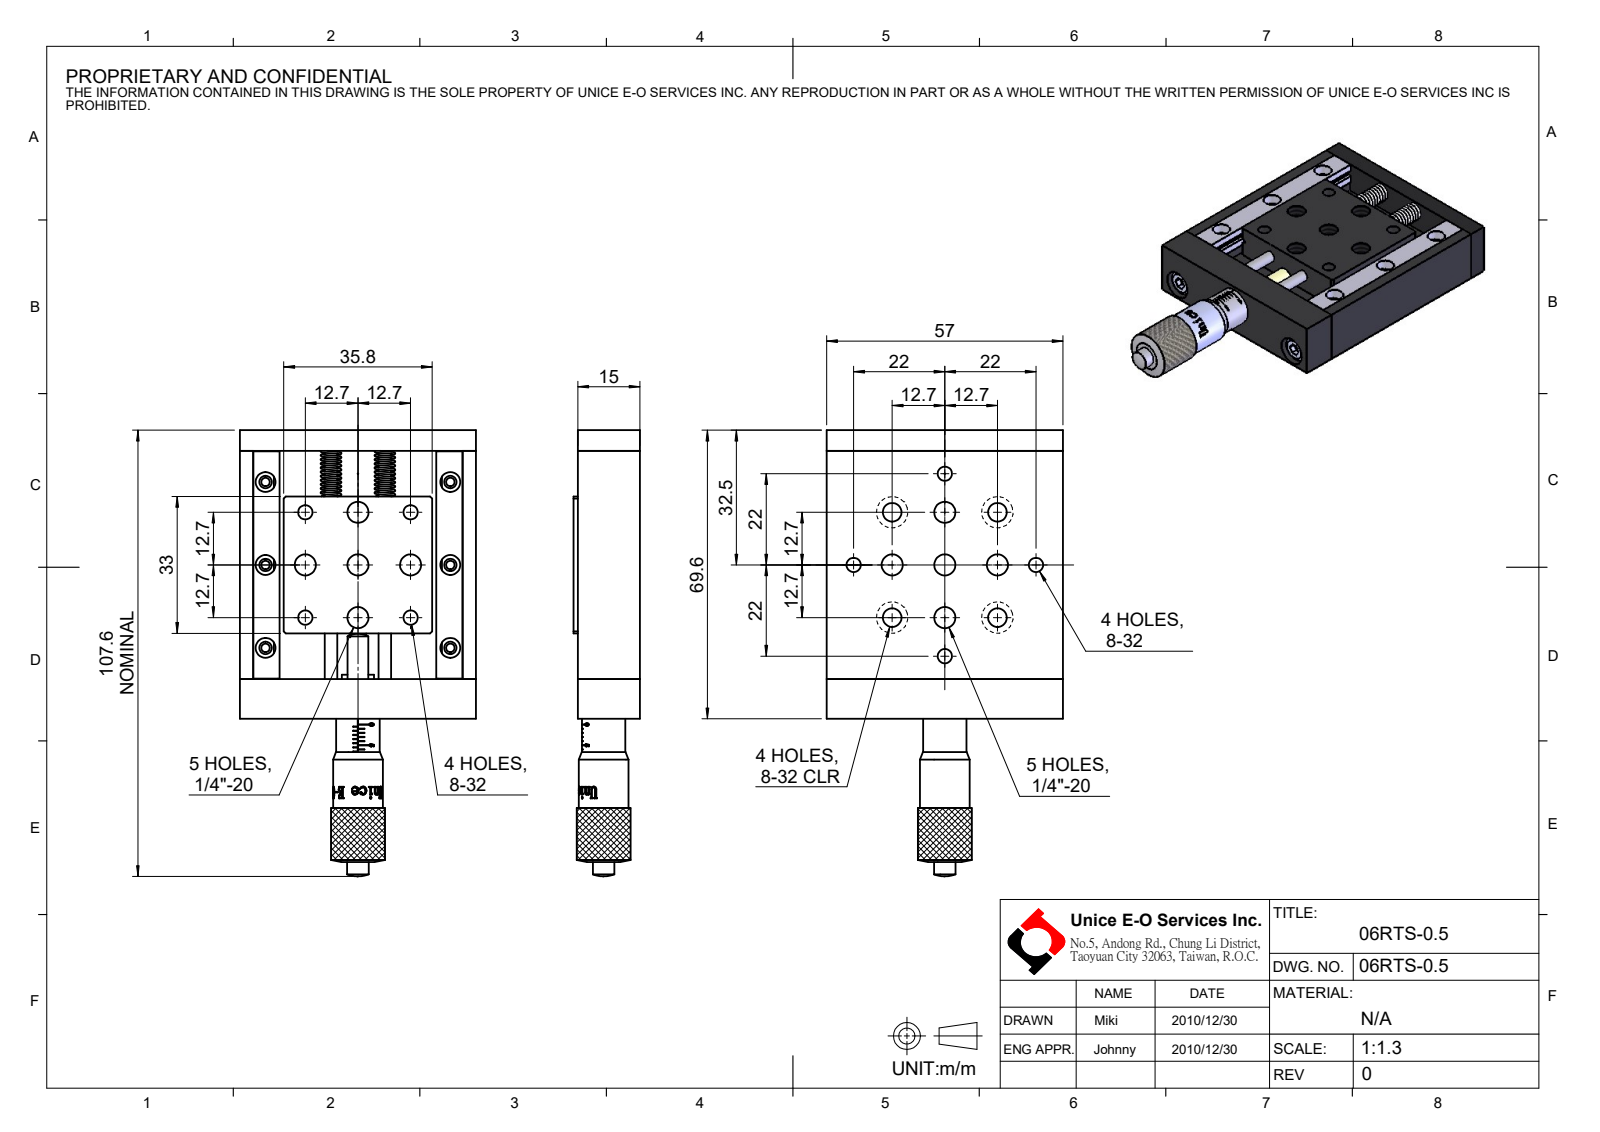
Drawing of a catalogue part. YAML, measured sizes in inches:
part_name: "06RTS-0.5"
step_written_by: "SolidWorks 2016 (CONFIG_CONTROL_DESIGN)"
units: inches
bodies: {solids: 16, faces: 747, planar: 360, cylindrical: 190, other: 197}
overall_size: [4.238, 2.244, 0.63]
volume: 3.136
surface_area: 51.55
round_holes:
  - {diameter: 0.118, count: 8}
  - {diameter: 0.136, count: 8}
  - {diameter: 0.081, count: 6}
  - {diameter: 0.189, count: 6}
  - {diameter: 0.201, count: 5}
  - {diameter: 0.098, count: 4}
  - {diameter: 0.177, count: 4}
  - {diameter: 0.297, count: 4}
  - {diameter: 0.197, count: 3}
  - {diameter: 0.122, count: 2}
  - {diameter: 0.13, count: 2}
  - {diameter: 0.177, count: 2}
round_bosses_or_shafts:
  - {diameter: 0.276, count: 2}
  - {diameter: 0.157, count: 2}
  - {diameter: 0.512, count: 1}
  - {diameter: 0.472, count: 1}
  - {diameter: 0.413, count: 1}
  - {diameter: 0.39, count: 1}
  - {diameter: 0.374, count: 1}
  - {diameter: 0.362, count: 1}
partial_cylinders:
  - {radius: 0.098, count: 1}
  - {radius: 0.235, count: 1}
face_to_face_distances: [0.354, 0.236, 0.039, 0.276, 0.591, 0.118, 0.63, 2.165, 0.378, 0.079]
hole_center_spacings: [1, 0.5, 0.787, 0.62, 0.707, 1.118, 1.455, 1.179]
